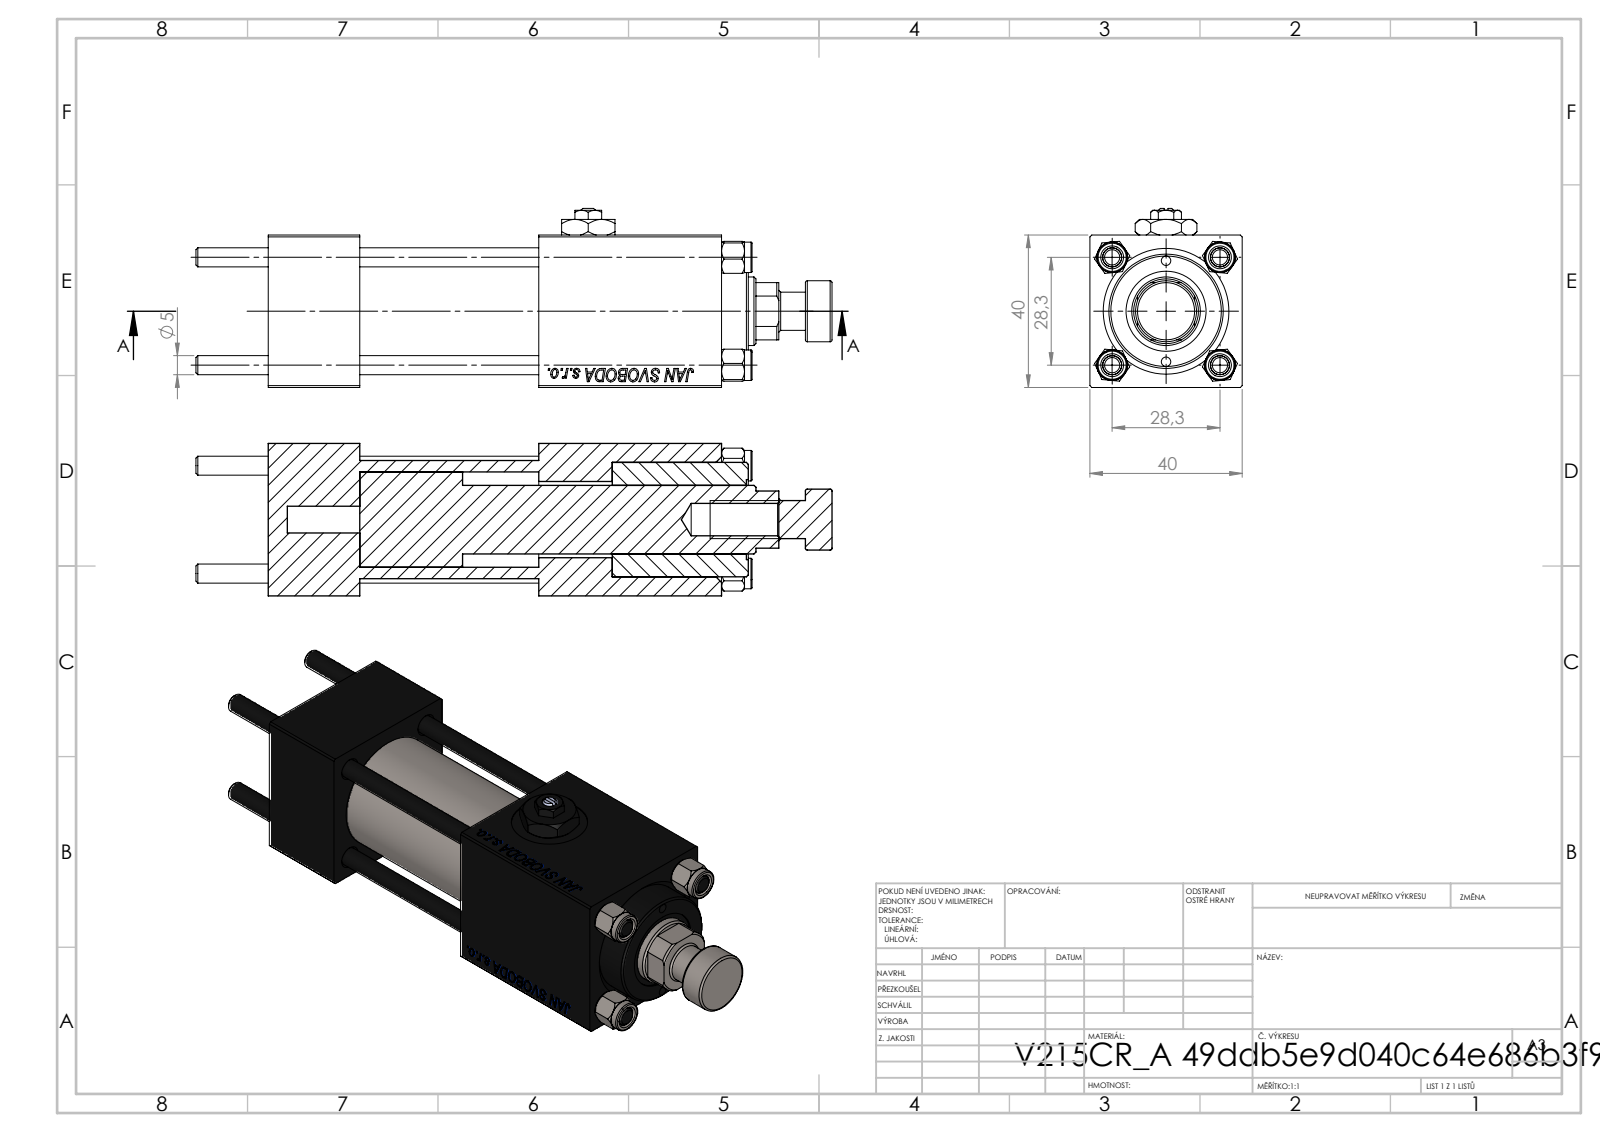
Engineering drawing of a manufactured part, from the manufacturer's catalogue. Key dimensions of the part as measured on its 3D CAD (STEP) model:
Part name (STEP PRODUCT): V215CR_BODY_A; V215CR_VCP; V215CR_ROD_END_W; CR025_012_A_0_G_A_G_M_020_+#_##_TYCINKA (+3 more)
STEP written by: SolidWorks 2019 (CONFIG_CONTROL_DESIGN)
Units: millimetres
Bodies: 13 solids, 1195 faces (545 planar, 88 cylindrical, 562 other)
Overall size (bounding box): 167 × 47 × 40
Volume: 153 618 mm³ · Surface area: 63 055 mm²
Round holes (diameter × count): ⌀5 ×4, ⌀20 ×3, ⌀2.5 ×2, ⌀7 ×2, ⌀13.16 ×2, ⌀8.5 ×1, ⌀18 ×1, ⌀21 ×1, ⌀25 ×1, ⌀30 ×1
Round bosses / shafts (diameter × count): ⌀8 ×4, ⌀31 ×1, ⌀16 ×1, ⌀10 ×1
Partial cylindrical surfaces — rounded edges, fillets, slot ends (radius × count): R8.5 ×1
Main face-to-face distances: 40, 24, 71, 47, 90.3, 66.3, 19.3, 119, 95, 48
Hole centre spacings: 14.18, 20.01, 28.3, 30.84, 13.25, 40.02, 26.5, 72
